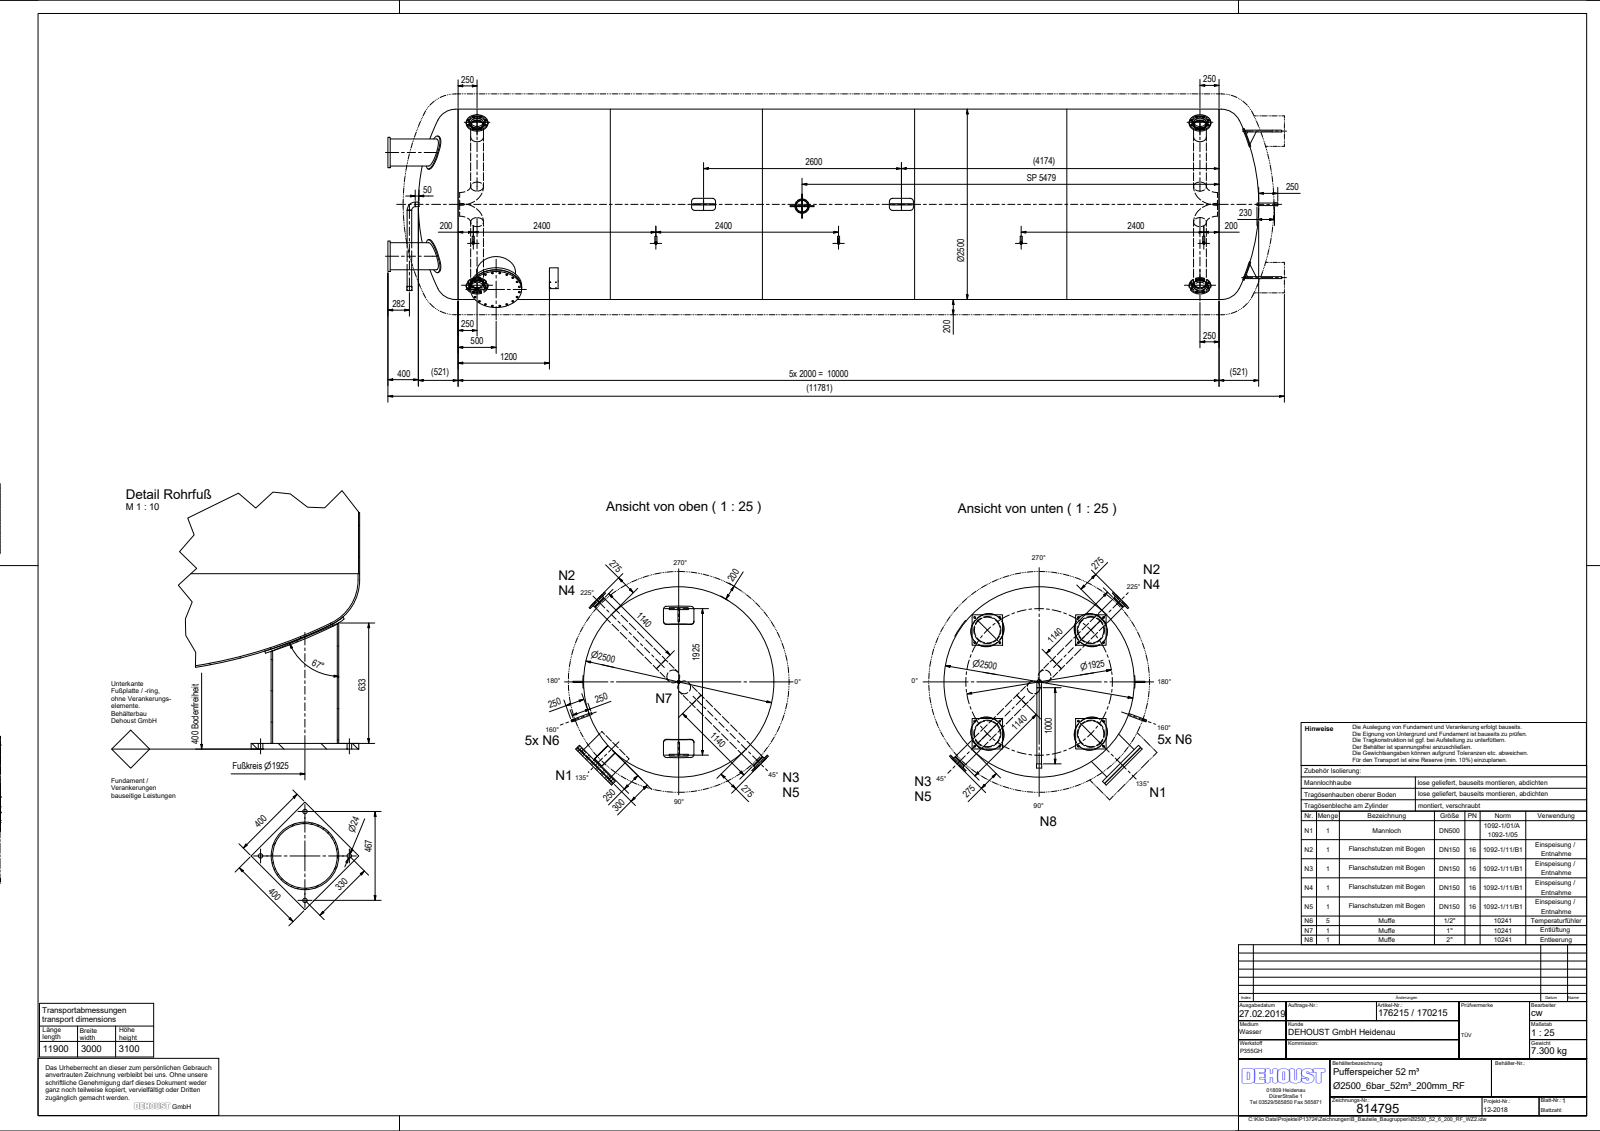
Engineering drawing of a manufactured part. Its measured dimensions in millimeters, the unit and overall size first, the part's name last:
Units: millimetres
Overall size (bounding box): 11745.05 × 2664.05 × 2604.82
Round holes (diameter × count): ⌀26 ×40, ⌀22 ×32, ⌀24 ×16, ⌀159.3 ×8, ⌀18.63 ×5, ⌀21.7 ×5, ⌀26.9 ×5, ⌀5.8 ×4, ⌀168.3 ×4, ⌀339.6 ×4, ⌀5 ×2, ⌀52.3 ×2
Round bosses / shafts (diameter × count): ⌀168.3 ×8, ⌀26.9 ×5, ⌀26.4 ×5, ⌀450 ×4, ⌀355.6 ×4, ⌀285 ×4, ⌀212 ×4, ⌀670 ×2
Partial cylindrical surfaces — rounded edges, fillets, slot ends (radius × count): R42 ×16, R6 ×8, R5 ×2, R10 ×2, R36 ×2, R72 ×2, R125 ×1, R1259 ×1
Main face-to-face distances: 600, 30, 5646.47, 6196.47, 5616.47, 6166.47, 550, 27.99, 4725, 5275
Hole centre spacings: 310, 120, 120.01, 191.59, 2400, 9500, 501.59, 4800
Volume: 868 300 000 mm³ · Surface area: 203 300 000 mm²
Bodies: 58 solids, 453 faces (178 planar, 225 cylindrical, 50 other)
Part name (STEP PRODUCT): Ø2500_52_6_200_RF_WZ2; Klöpper_Gew_Ø2500_8,3; Zyl_Ø2500_6x10000_2019; TÖB_Puffer_Ø2500_8, 3_200 (+8 more)
STEP written by: Autodesk Inventor 2019 (AUTOMOTIVE_DESIGN)
